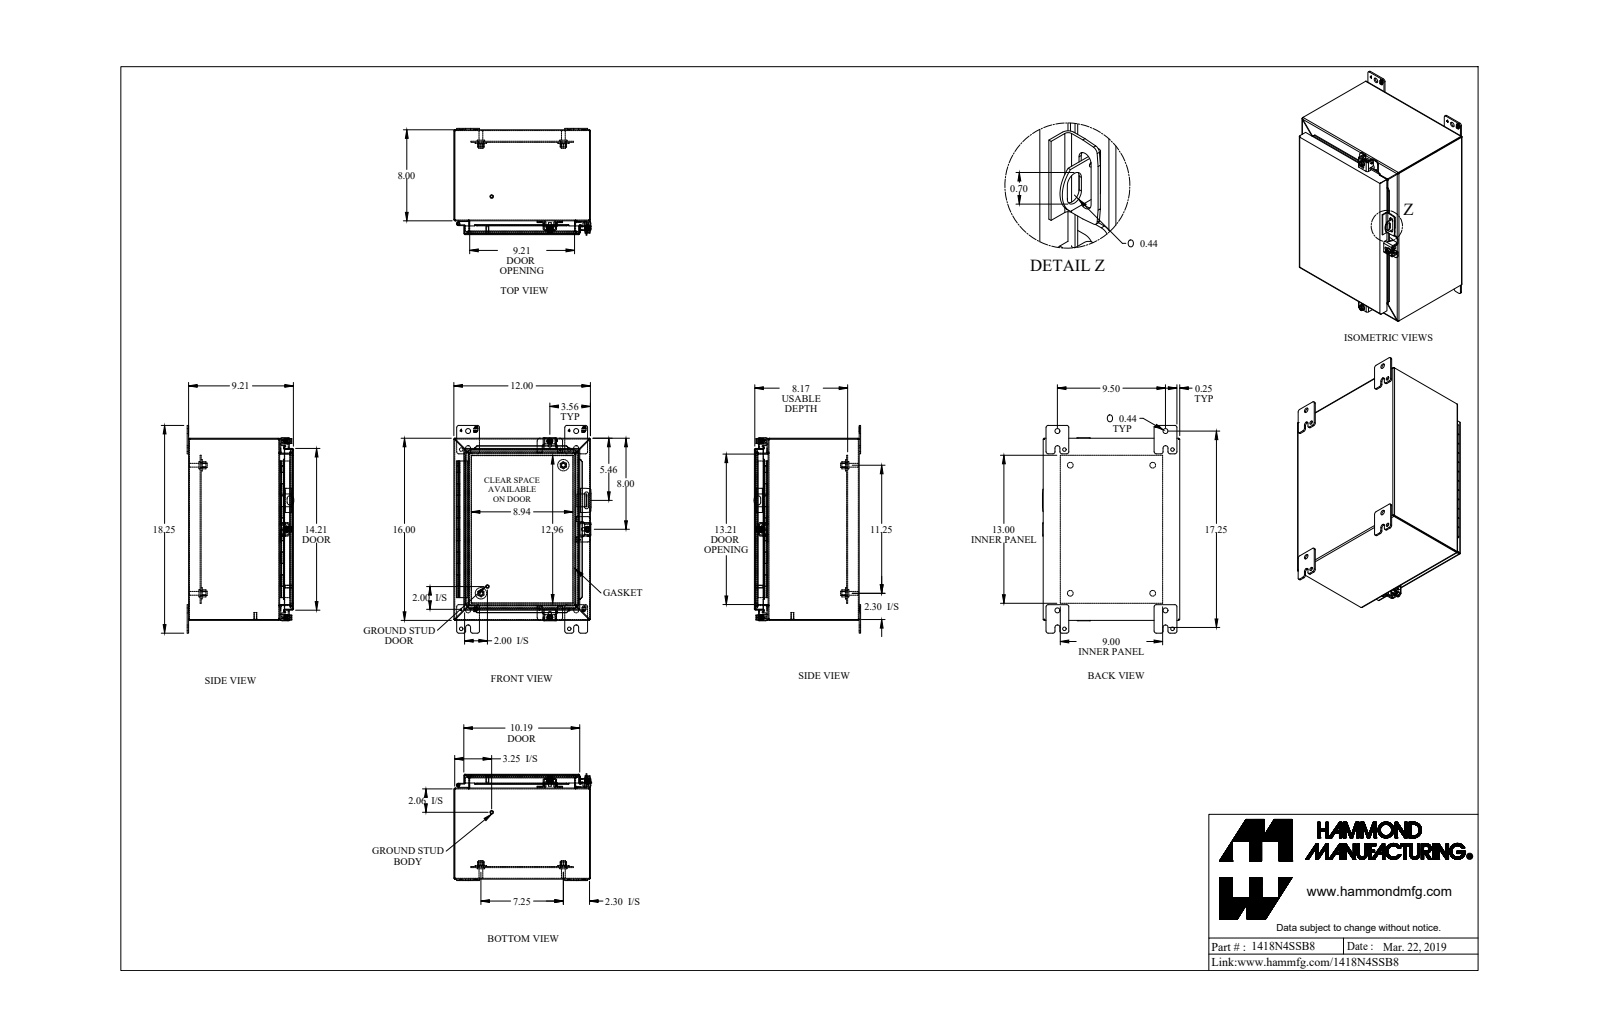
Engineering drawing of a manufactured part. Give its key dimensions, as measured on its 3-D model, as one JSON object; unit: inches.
{"part_name": "1418N4SSB8_Default", "step_written_by": "SolidWorks 2019 (CONFIG_CONTROL_DESIGN)", "units": "inches", "bodies": {"solids": 35, "faces": 1283, "planar": 801, "cylindrical": 392, "other": 90}, "overall_size": [18.25, 12.063, 9.375], "volume_in3": 89.34, "surface_area_in2": 2388, "round_holes": [[0.313, 4], [0.437, 4], [0.5, 4], [0.213, 3], [0.265, 3], [0.375, 3], [0.307, 2], [0.445, 2], [0.125, 1], [0.187, 1]], "round_bosses_or_shafts": [[0.65, 4], [0.375, 4], [0.332, 4], [0.5, 3], [0.39, 3], [0.244, 3], [1, 2], [0.313, 2]], "partial_cylinders_radius": [[0.188, 26], [0.036, 24], [0.108, 24], [0.25, 16], [0.048, 15], [0.143, 15], [0.045, 8], [0.125, 8]], "face_to_face_distances": [0.072, 11.928, 15.928, 9.066, 9.138, 0.072, 9.138, 9.21, 0.937, 7.928], "hole_center_spacings": [1.735, 9.5, 15.75, 18.393, 2.434, 7.25, 3.204, 6.013]}
